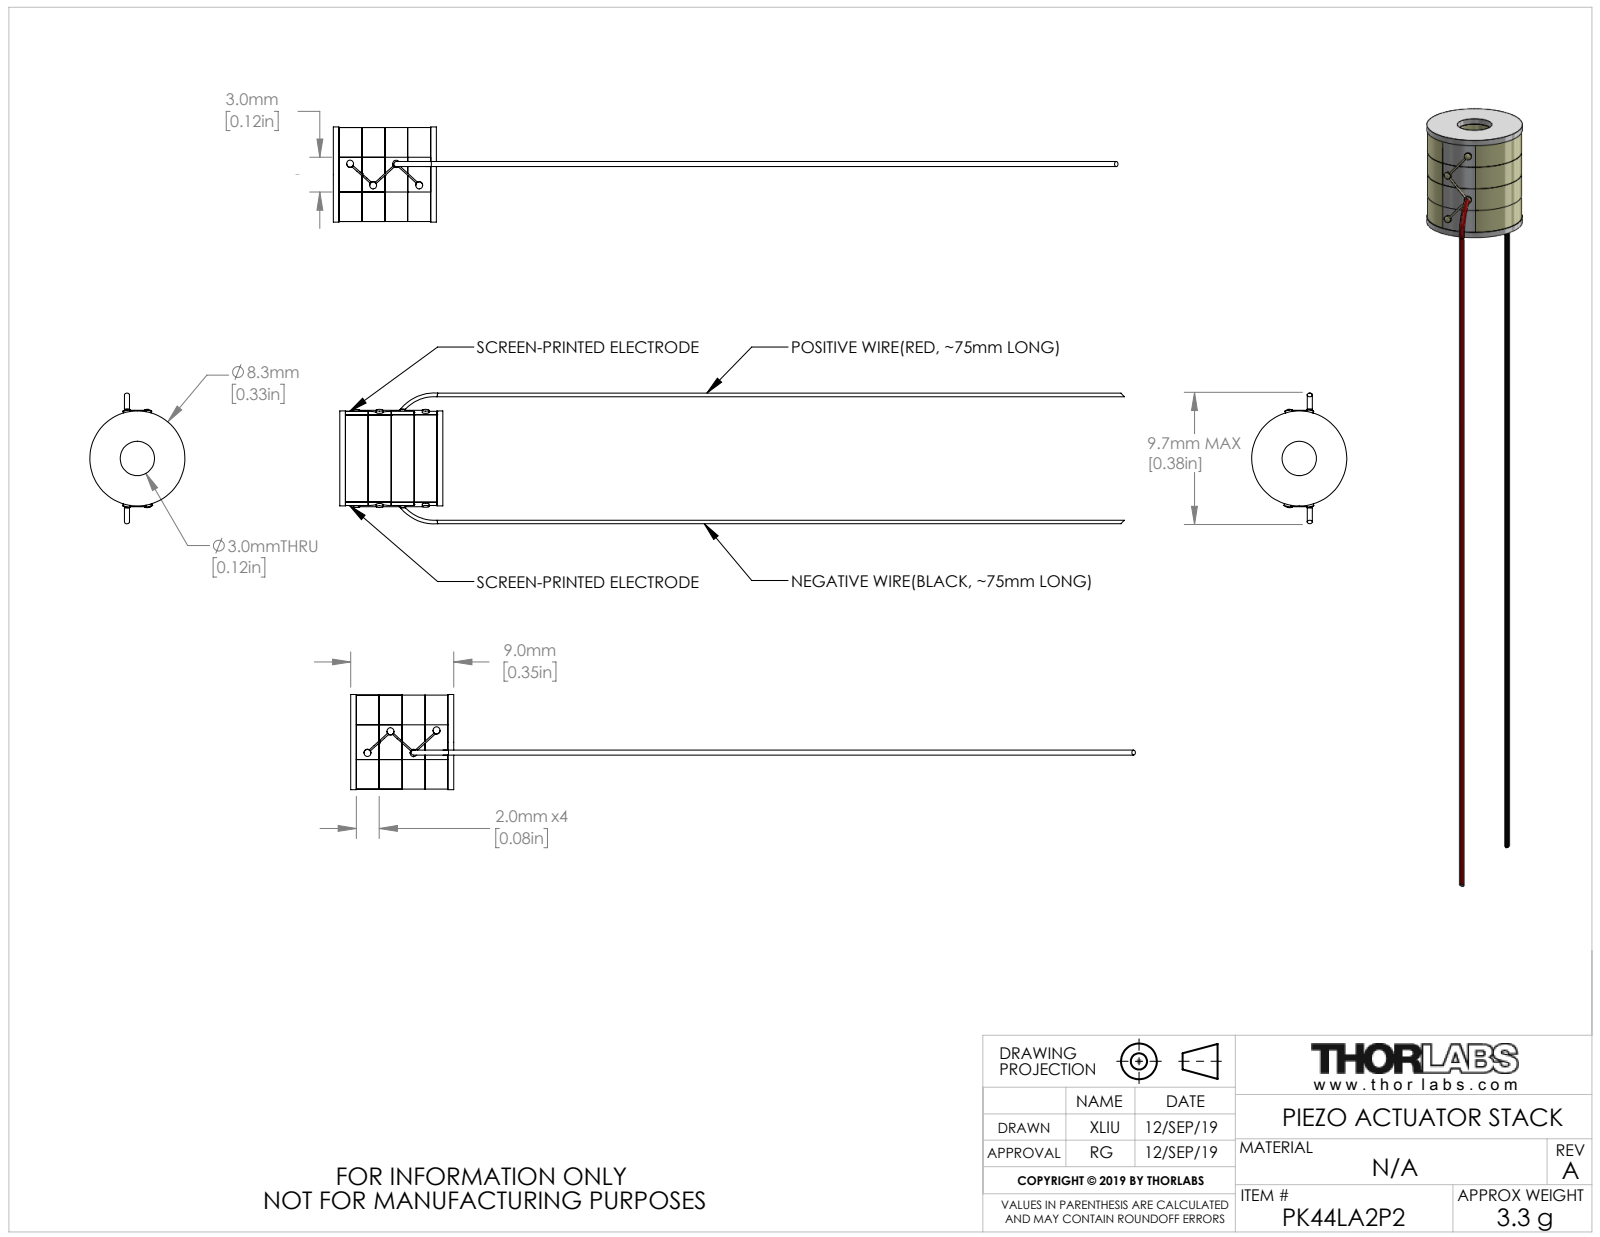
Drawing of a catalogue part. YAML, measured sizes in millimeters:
part_name: "CTN009777"
step_written_by: "SolidWorks 2016 (AUTOMOTIVE_DESIGN)"
units: millimeters
bodies: {solids: 8, faces: 158, planar: 62, cylindrical: 52, other: 44}
overall_size: [68.52, 11.43, 8.3]
volume: 611
surface_area: 1356
round_holes:
  - {diameter: 3, count: 1}
round_bosses_or_shafts:
  - {diameter: 8.3, count: 1}
  - {diameter: 8.2, count: 1}
partial_cylinders:
  - {radius: 4.11, count: 1}
face_to_face_distances: [2, 4, 6, 0.5, 2.5, 4.5, 6.5, 8.5, 8, 9]
